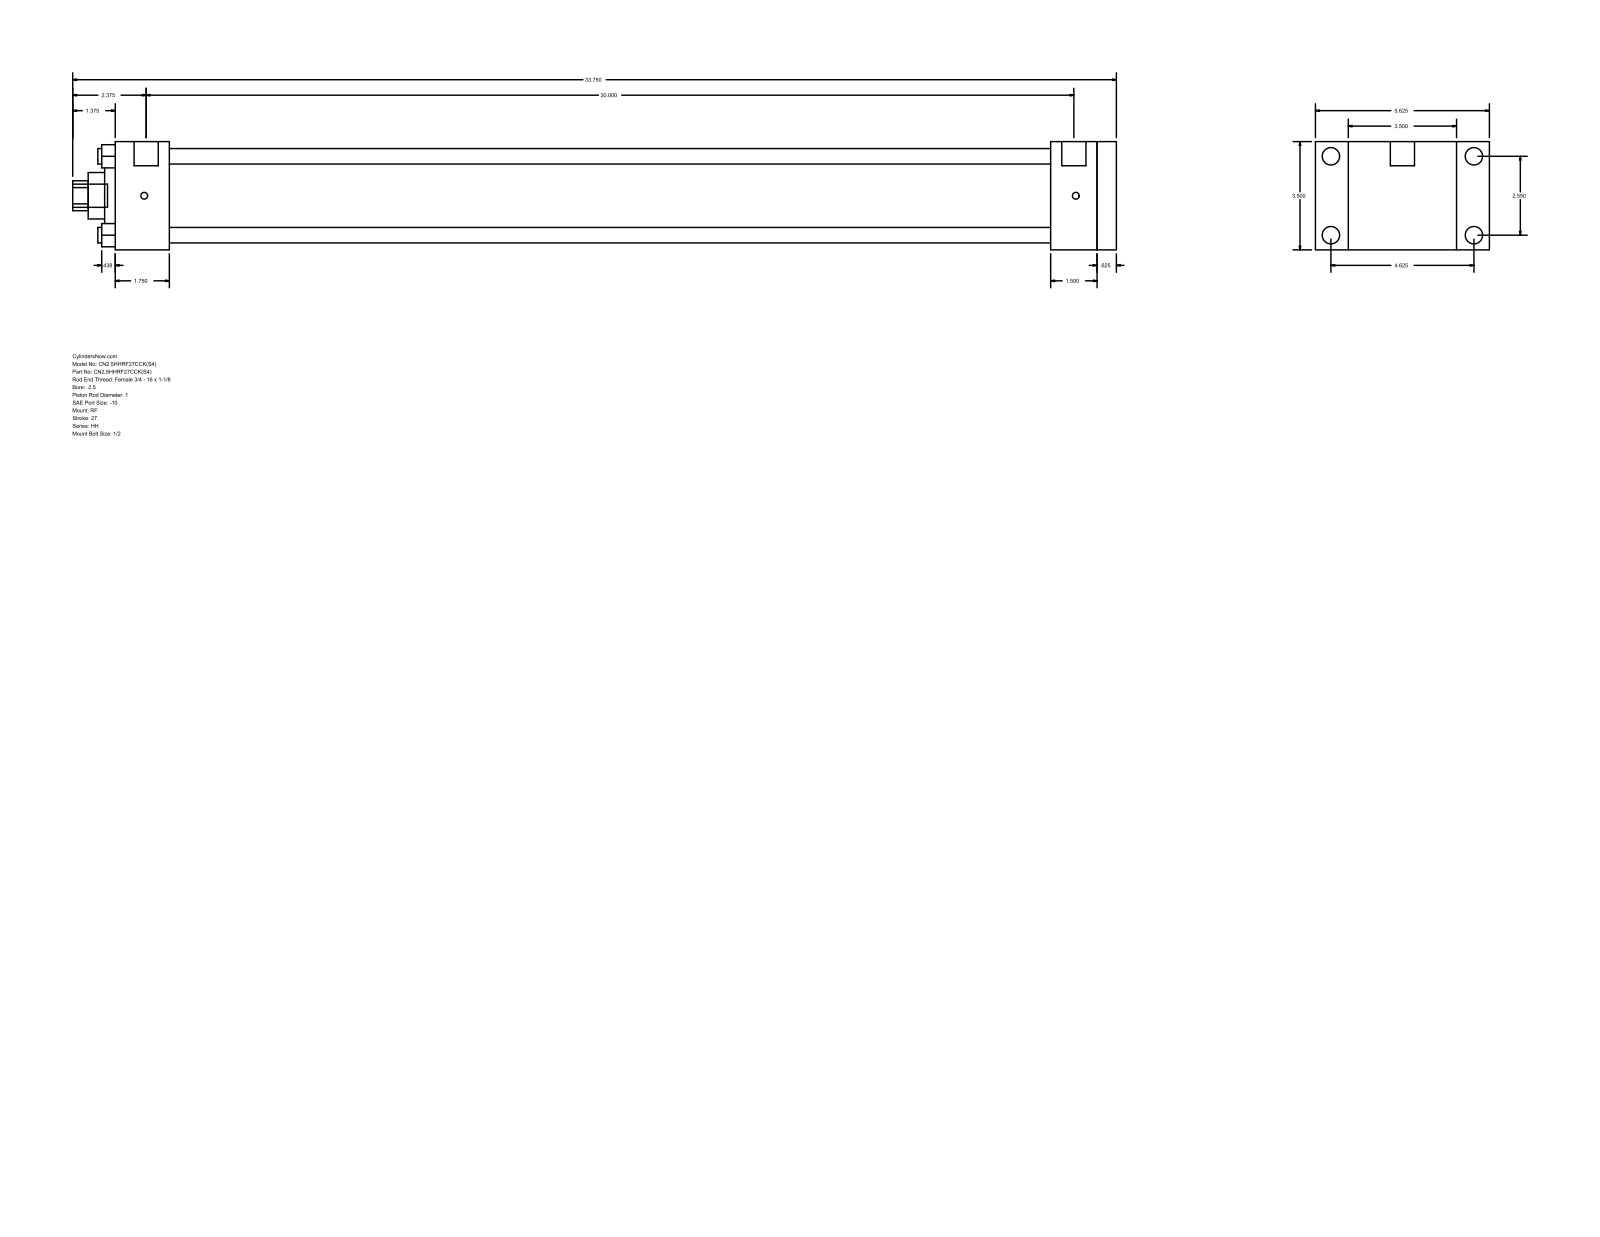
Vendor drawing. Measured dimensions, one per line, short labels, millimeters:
name: HH_RF__0250_1
written by: GSSL Pune (CONFIG_CONTROL_DESIGN)
unit: mm
bodies: 0 solids, 94 faces (65 planar, 29 cylindrical, 0 other)
size: 857.25 × 142.88 × 88.9
holes: 4× ⌀12.7, 1× ⌀25.4, 1× ⌀38.1, 1× ⌀60.33, 1× ⌀73.03
bosses: 4× ⌀14.3, 4× ⌀5.56, 2× ⌀19.84, 1× ⌀19.05
rounds: 1× R12.29
face distances: 88.9, 15.87, 806.46, 822.33, 44.46, 762, 777.87, 768.35, 723.89, 38.11
hole spacings: 45.79, 64.76, 91.58
